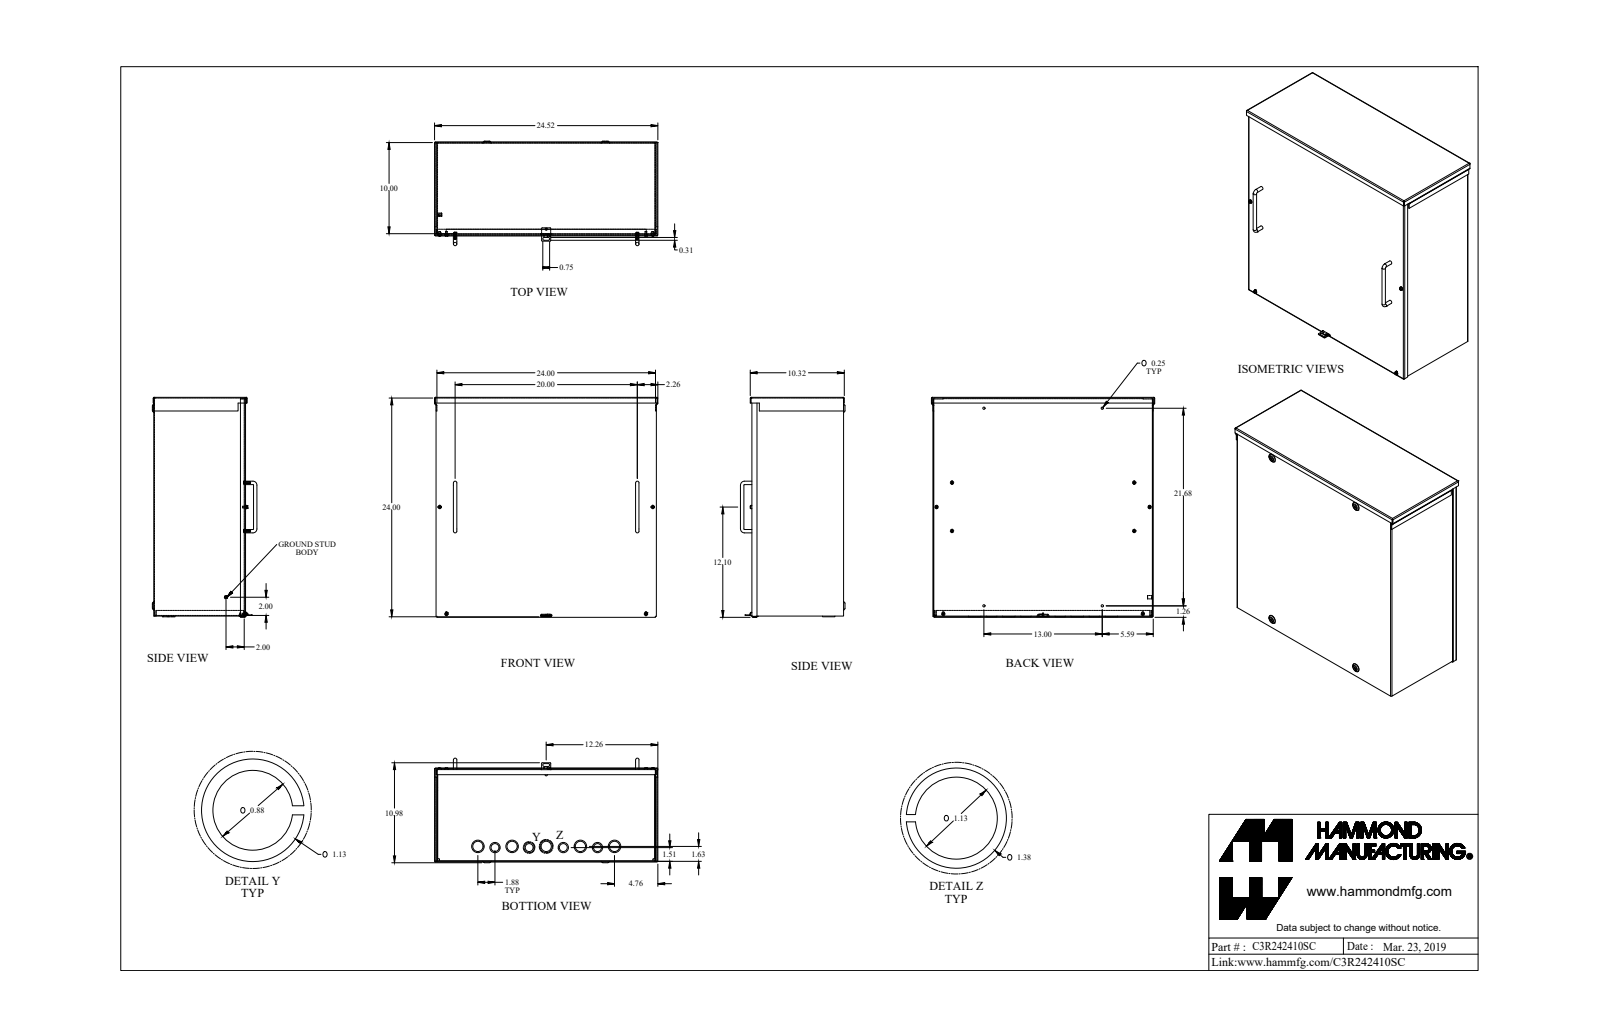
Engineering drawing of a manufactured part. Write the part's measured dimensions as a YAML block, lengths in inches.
part_name: "C3R242410SC_Default"
step_written_by: "SolidWorks 2019 (CONFIG_CONTROL_DESIGN)"
units: inches
bodies: {solids: 17, faces: 609, planar: 314, cylindrical: 177, other: 118}
overall_size: [24.519, 24.135, 11.478]
volume: 165.2
surface_area: 4592
round_holes:
  - {diameter: 0.156, count: 5}
  - {diameter: 0.17, count: 4}
  - {diameter: 0.203, count: 4}
  - {diameter: 0.25, count: 4}
  - {diameter: 1.125, count: 3}
  - {diameter: 0.875, count: 2}
  - {diameter: 0.875, count: 2}
  - {diameter: 1.125, count: 2}
  - {diameter: 0.125, count: 1}
  - {diameter: 0.137, count: 1}
round_bosses_or_shafts:
  - {diameter: 0.375, count: 9}
  - {diameter: 0.19, count: 8}
  - {diameter: 1.125, count: 4}
  - {diameter: 0.367, count: 4}
  - {diameter: 1.375, count: 3}
  - {diameter: 1.375, count: 2}
  - {diameter: 0.375, count: 2}
  - {diameter: 0.125, count: 1}
partial_cylinders:
  - {radius: 0.036, count: 20}
  - {radius: 0.108, count: 20}
  - {radius: 0.109, count: 8}
  - {radius: 0.125, count: 8}
  - {radius: 0.156, count: 2}
  - {radius: 0.029, count: 1}
  - {radius: 0.086, count: 1}
face_to_face_distances: [0.072, 10, 23.928, 9.928, 10.072, 24, 0.072, 23.856, 23.856, 23.928]
hole_center_spacings: [20, 3.75, 0.024, 1.879, 1.88, 3.146, 5.3, 5.627]
